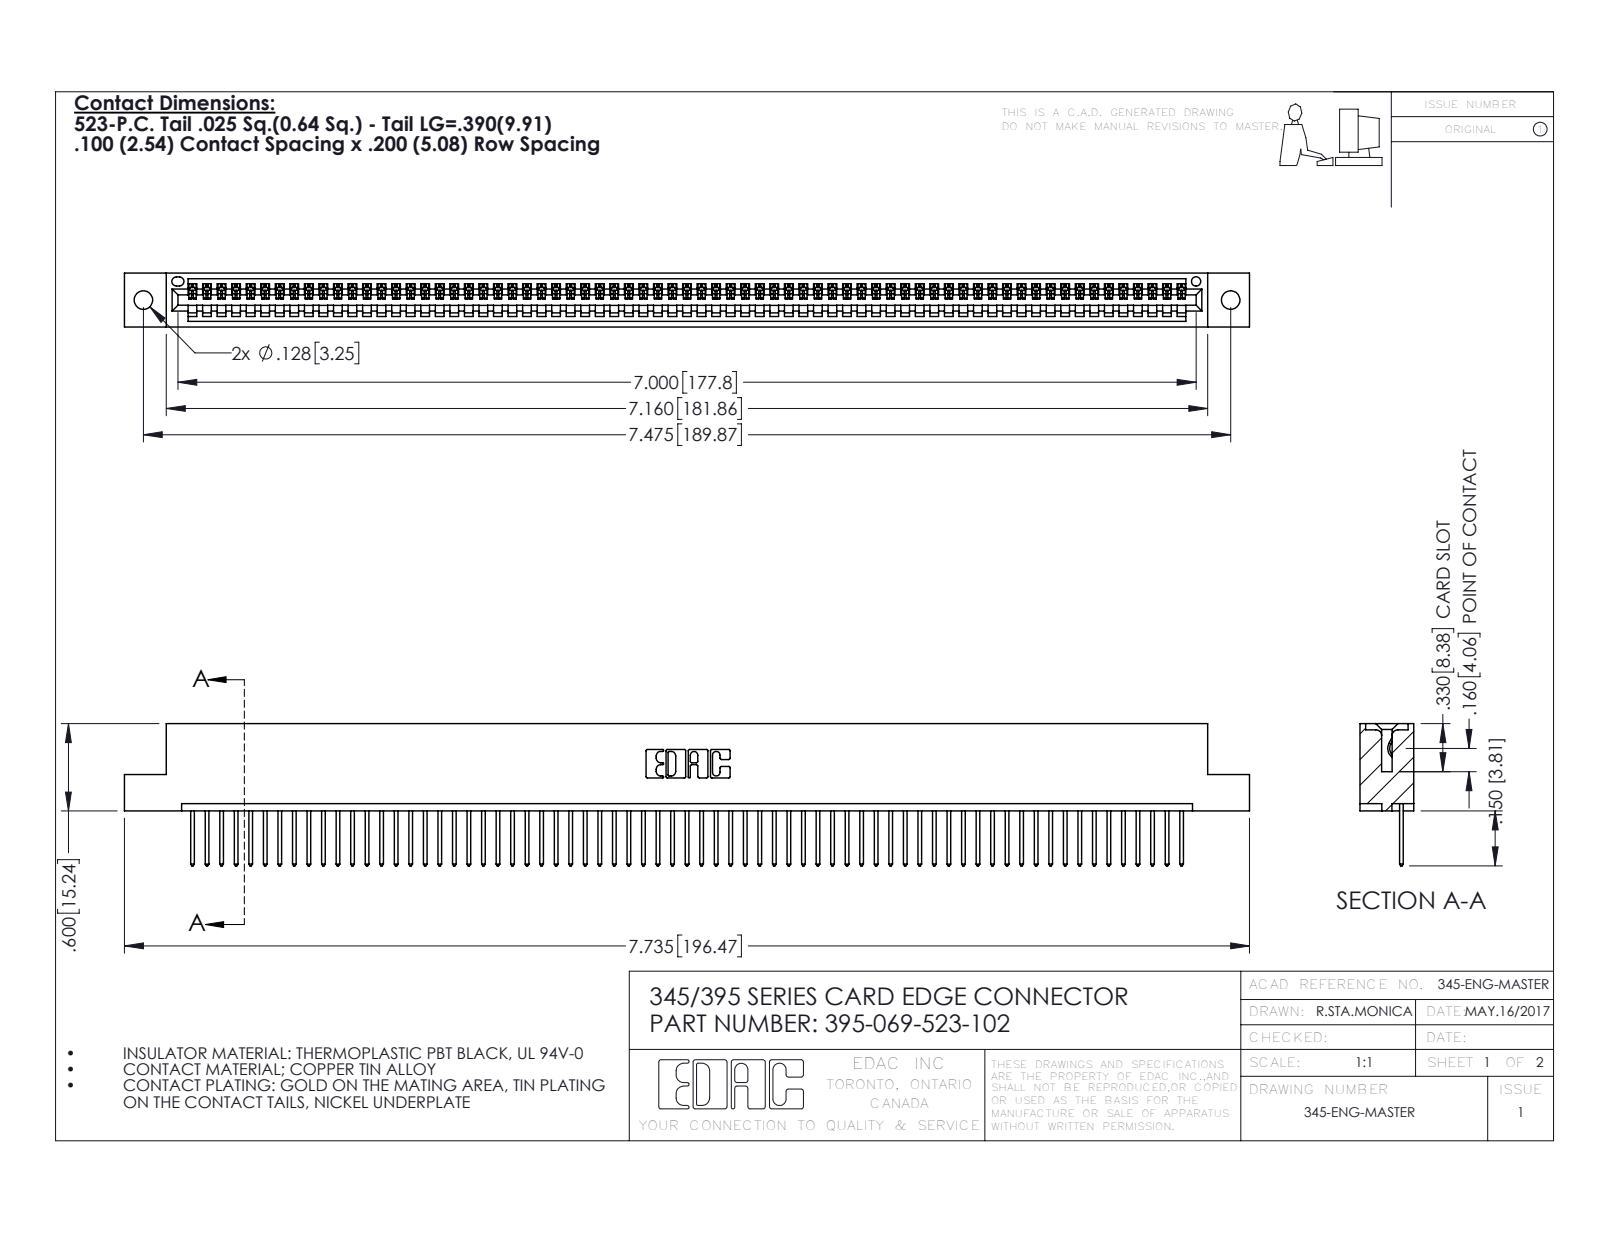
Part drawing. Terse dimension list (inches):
name: 395-069-523-102; 345 Part_Flush Mounting Lugs - 0.128 Dia; 345-292-001_345-293-123
written by: SolidWorks 2016 (CONFIG_CONTROL_DESIGN)
unit: in
bodies: 70 solids, 4128 faces (2840 planar, 1288 cylindrical, 0 other)
size: 7.735 × 0.977 × 0.37
volume: 1.148 in³; area: 39.03 in²
holes: 2× ⌀0.128, 1× ⌀0.064
rounds: 138× R0.006, 138× R0.01, 22× R0.01, 6× R0.007, 6× R0.031, 3× R0.026, 2× R0.031, 2× R0.04
face distances: 0.298, 0.072, 0.37, 0.2, 0.098, 0.272, 0.025, 0.225, 0.149, 0.072
hole spacings: 0.27, 7.239, 7.475
